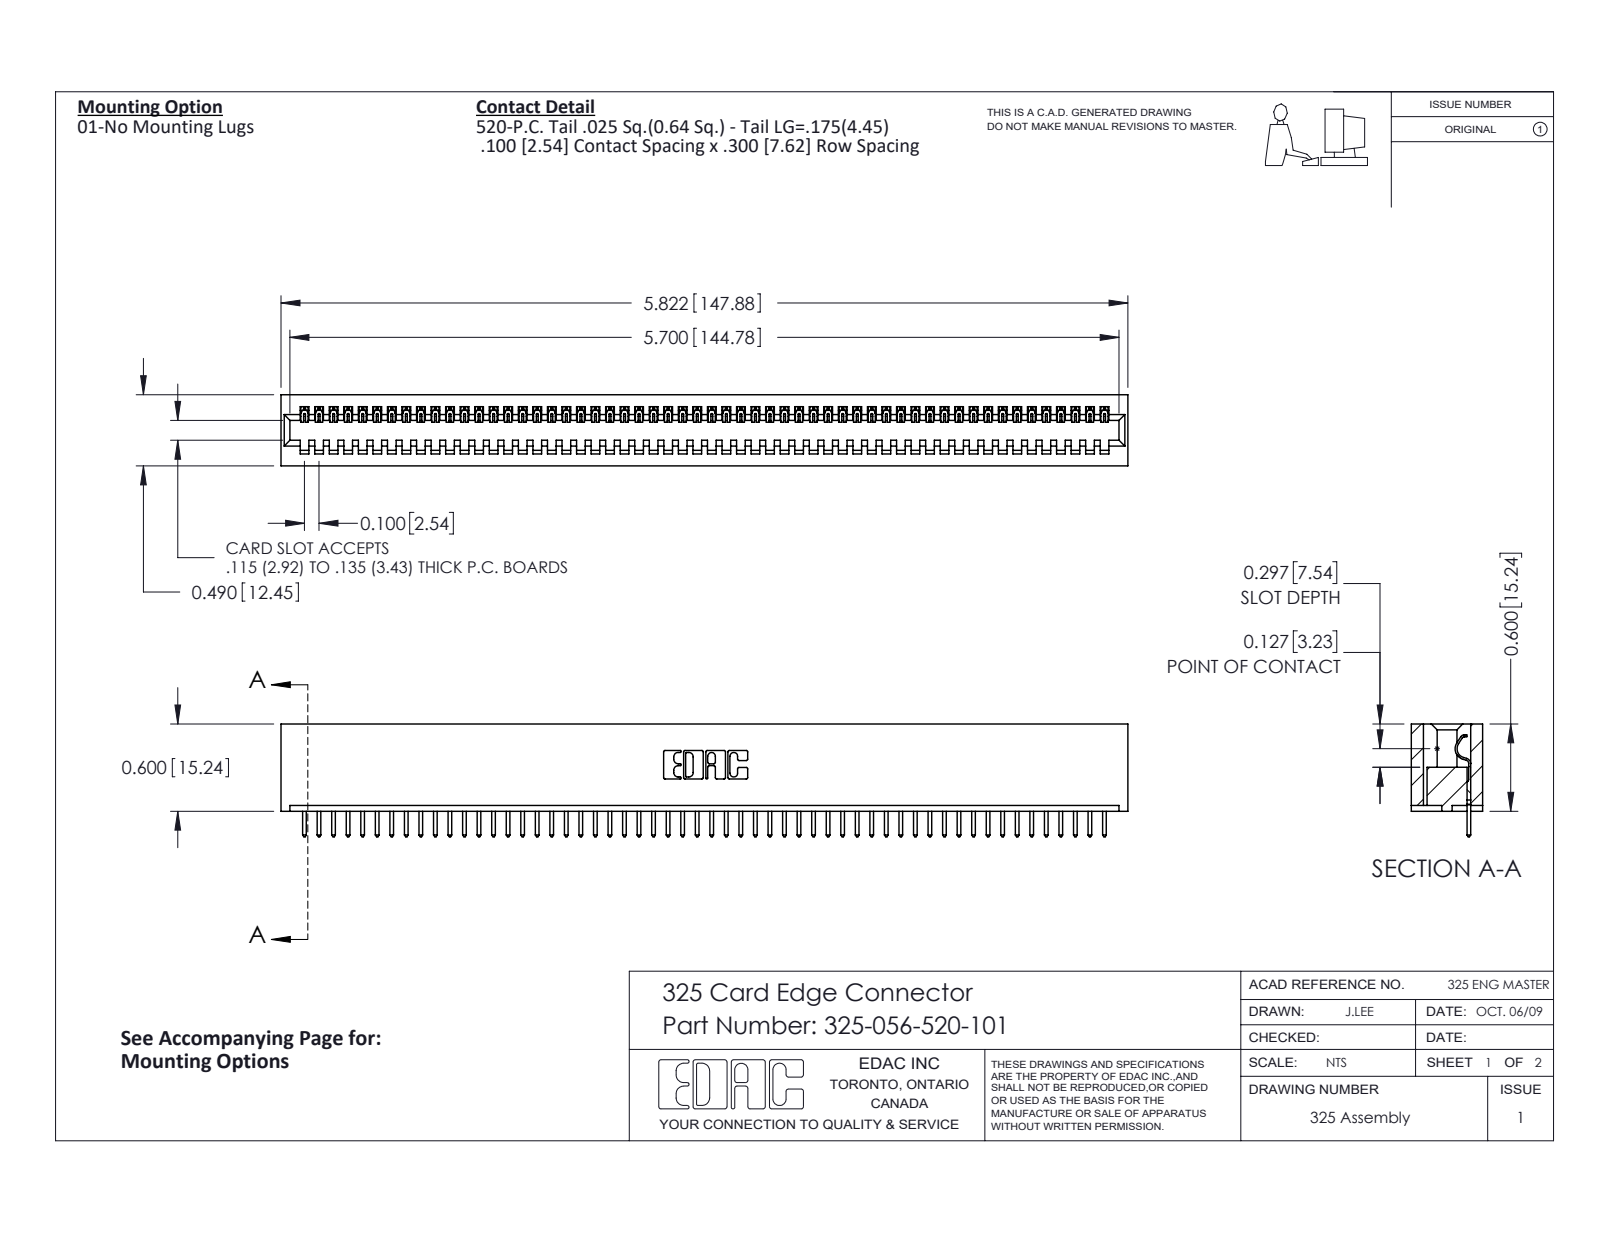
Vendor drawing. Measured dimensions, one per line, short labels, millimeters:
name: 325-292-001_325-293-120; 325-056-520-101; 325 Part_Lugless
written by: SolidWorks 2016 (CONFIG_CONTROL_DESIGN)
unit: mm
bodies: 57 solids, 3354 faces (2418 planar, 936 cylindrical, 0 other)
size: 147.9 × 19.7 × 12.4
volume: 19 300 mm³; area: 21 240 mm²
rounds: 112× R0.2, 112× R0.3, 22× R0.3, 6× R0.2, 6× R0.8, 3× R0.7, 1× R0.4, 1× R0.6
face distances: 2.1, 10.3, 12.4, 7.6, 2.7, 9.7, 0.6, 8.3, 6.7, 14.2
